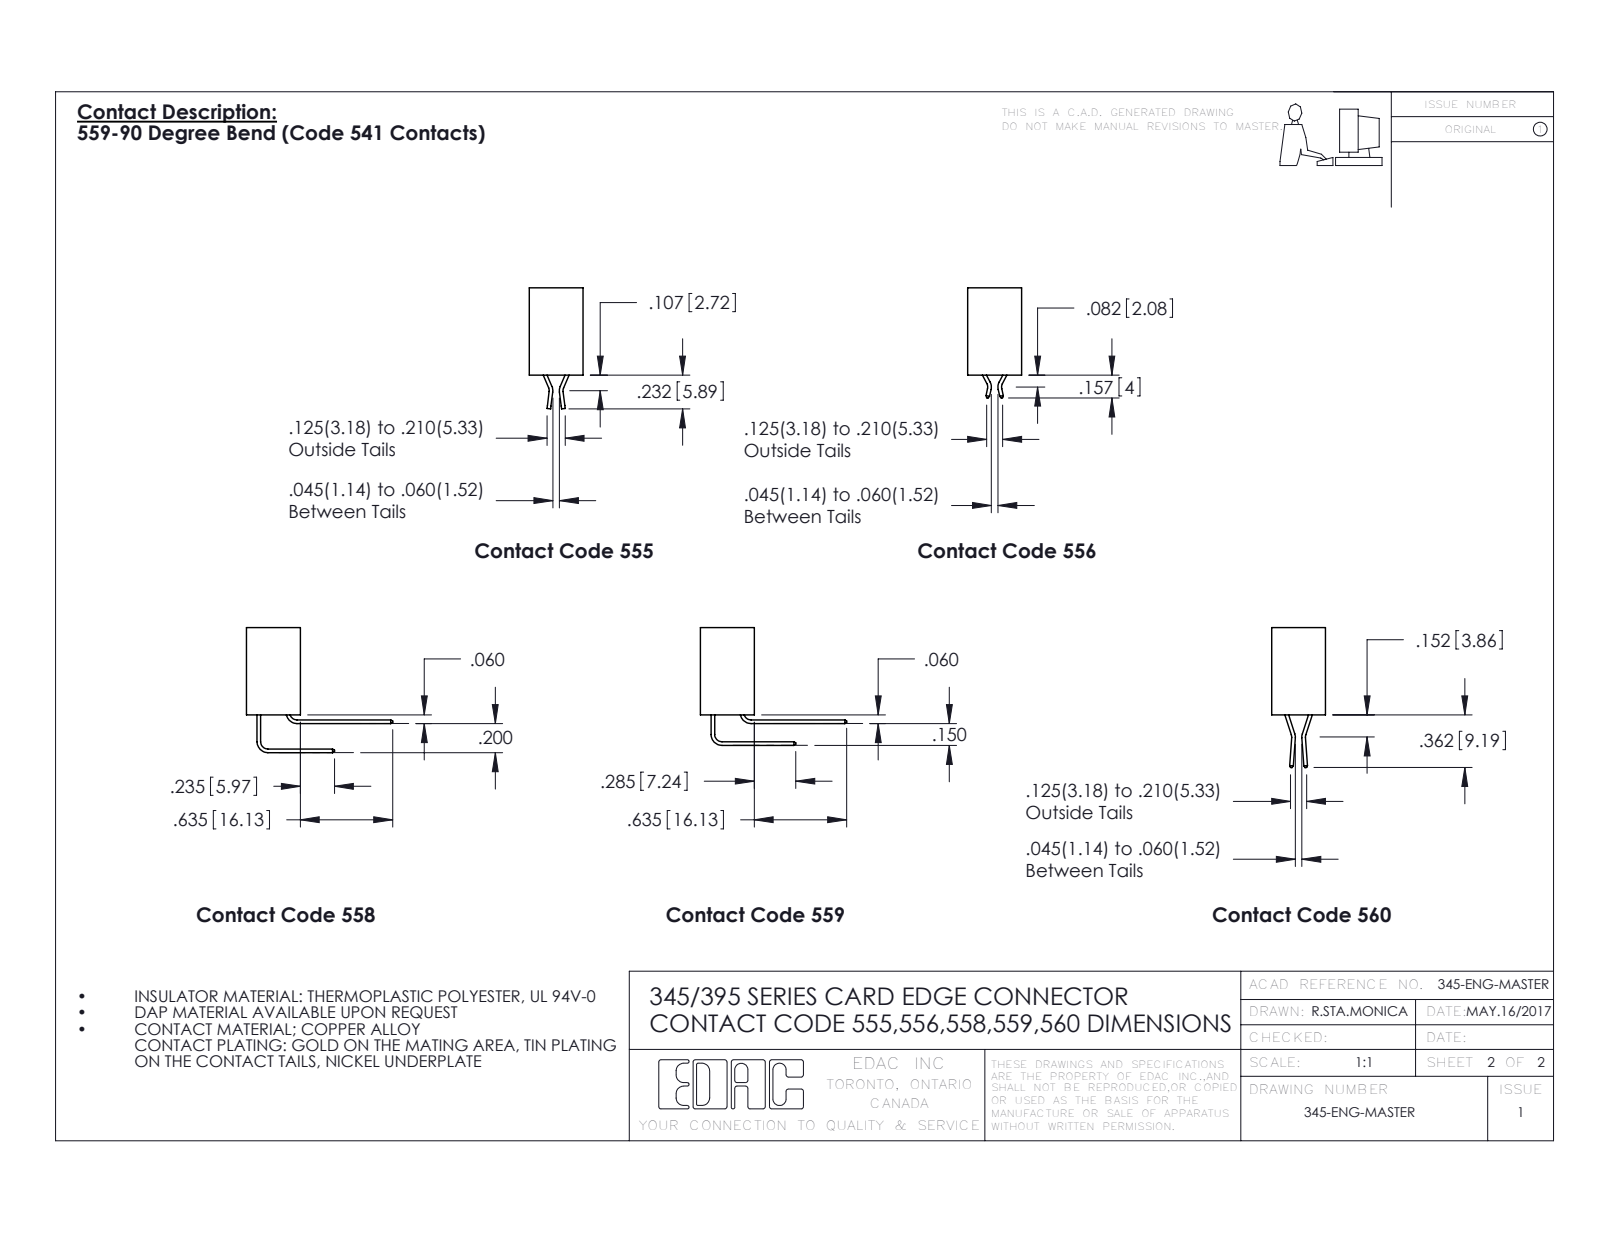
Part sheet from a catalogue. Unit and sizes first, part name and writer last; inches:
Units: inches
Overall size (bounding box): 1.735 × 1.005 × 0.659
Round holes (diameter × count): ⌀0.128 ×2, ⌀0.064 ×1
Partial cylindrical surfaces — rounded edges, fillets, slot ends (radius × count): R0.01 ×22, R0.006 ×18, R0.007 ×6, R0.031 ×6, R0.026 ×3, R0.031 ×2, R0.04 ×2, R0.014 ×1
Main face-to-face distances: 0.2, 0.37, 0.072, 0.298, 0.1, 0.098, 0.272, 0.025, 0.6, 0.06
Hole centre spacings: 1.475
Volume: 0.231 in³ · Surface area: 7.281 in²
Bodies: 10 solids, 670 faces (462 planar, 208 cylindrical, 0 other)
Part name (STEP PRODUCT): 345-292-001_558 559 Tail - 1; 345 Part_0.110 Offset - Side Mount; 395-009-559-412
STEP written by: SolidWorks 2016 (CONFIG_CONTROL_DESIGN)
